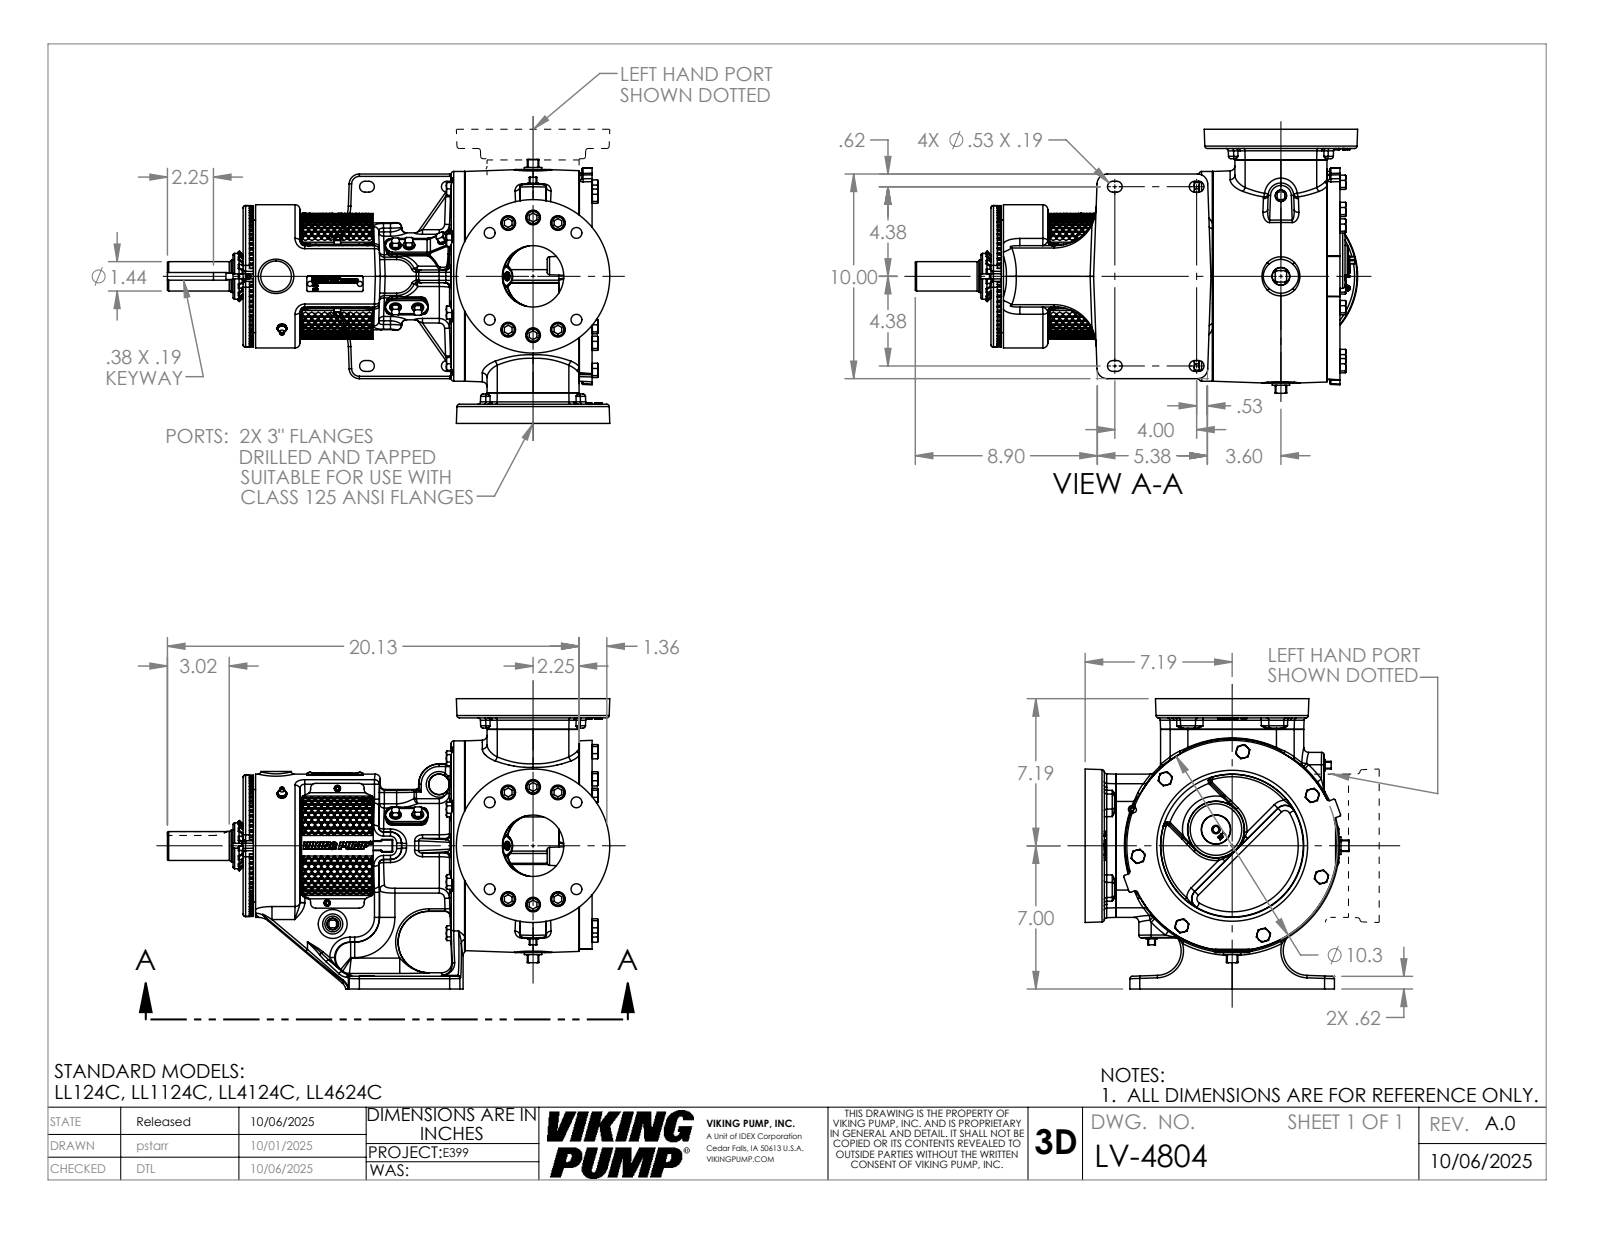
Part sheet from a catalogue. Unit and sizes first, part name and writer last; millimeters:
Units: millimetres
Overall size (bounding box): 549.27 × 360.36 × 327.72
Round holes (diameter × count): ⌀18.26 ×12, ⌀6.35 ×9, ⌀13.49 ×8, ⌀27.79 ×8, ⌀4.04 ×3, ⌀6.76 ×2, ⌀7.94 ×2, ⌀76.2 ×2, ⌀11.51 ×1, ⌀40.07 ×1, ⌀40.46 ×1, ⌀133.35 ×1
Round bosses / shafts (diameter × count): ⌀16.76 ×12, ⌀15.88 ×10, ⌀15.87 ×5, ⌀7.92 ×3, ⌀4.83 ×3, ⌀260.35 ×1, ⌀177.8 ×1, ⌀139.62 ×1
Partial cylindrical surfaces — rounded edges, fillets, slot ends (radius × count): R1.61 ×109, R3.05 ×84, R1.75 ×74, R0.25 ×66, R6.1 ×48, R0.76 ×18, R1.52 ×16, R6.35 ×14
Main face-to-face distances: 360.36, 363.47, 12.7, 57.15, 23.87, 89.91, 273.56, 9.23, 33.1, 25.4
Hole centre spacings: 76.2, 107.76, 73.02, 26.1, 31.61, 55.37, 57.18, 85.63
Volume: 15 880 000 mm³ · Surface area: 870 421 mm²
Bodies: 1 solid, 5006 faces (1497 planar, 973 cylindrical, 2536 other)
Part name (STEP PRODUCT): LV-4804
STEP written by: SolidWorks 2024 (AUTOMOTIVE_DESIGN)
